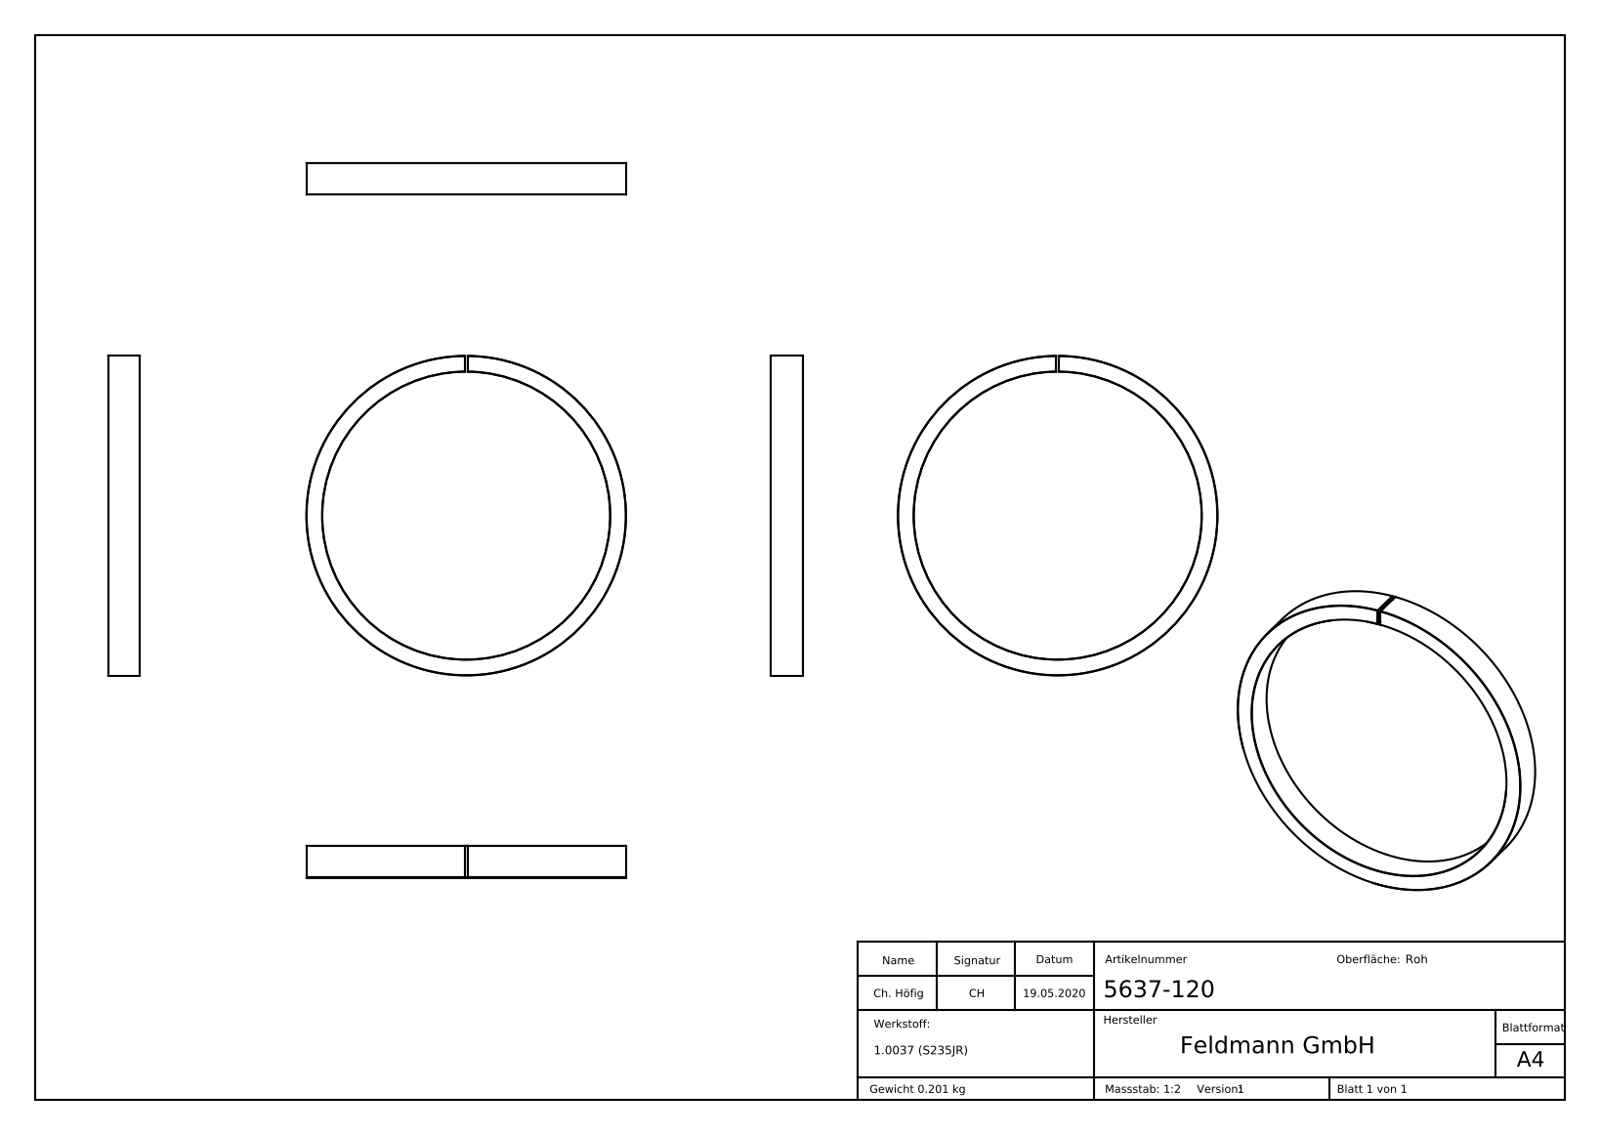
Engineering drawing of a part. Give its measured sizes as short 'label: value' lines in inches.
name: 5637-120
written by: SolidWorks 2015 (CONFIG_CONTROL_DESIGN)
unit: in
bodies: 1 solid, 209 faces (113 planar, 2 cylindrical, 94 other)
size: 4.724 × 4.724 × 0.472
volume: 1.569 in³; area: 20.16 in²
holes: 1× ⌀4.252
bosses: 1× ⌀4.724
face distances: 0.472, 0.039, 0.043, 0.07, 0.033, 0.083, 0.096, 0.039, 0.109, 0.048
